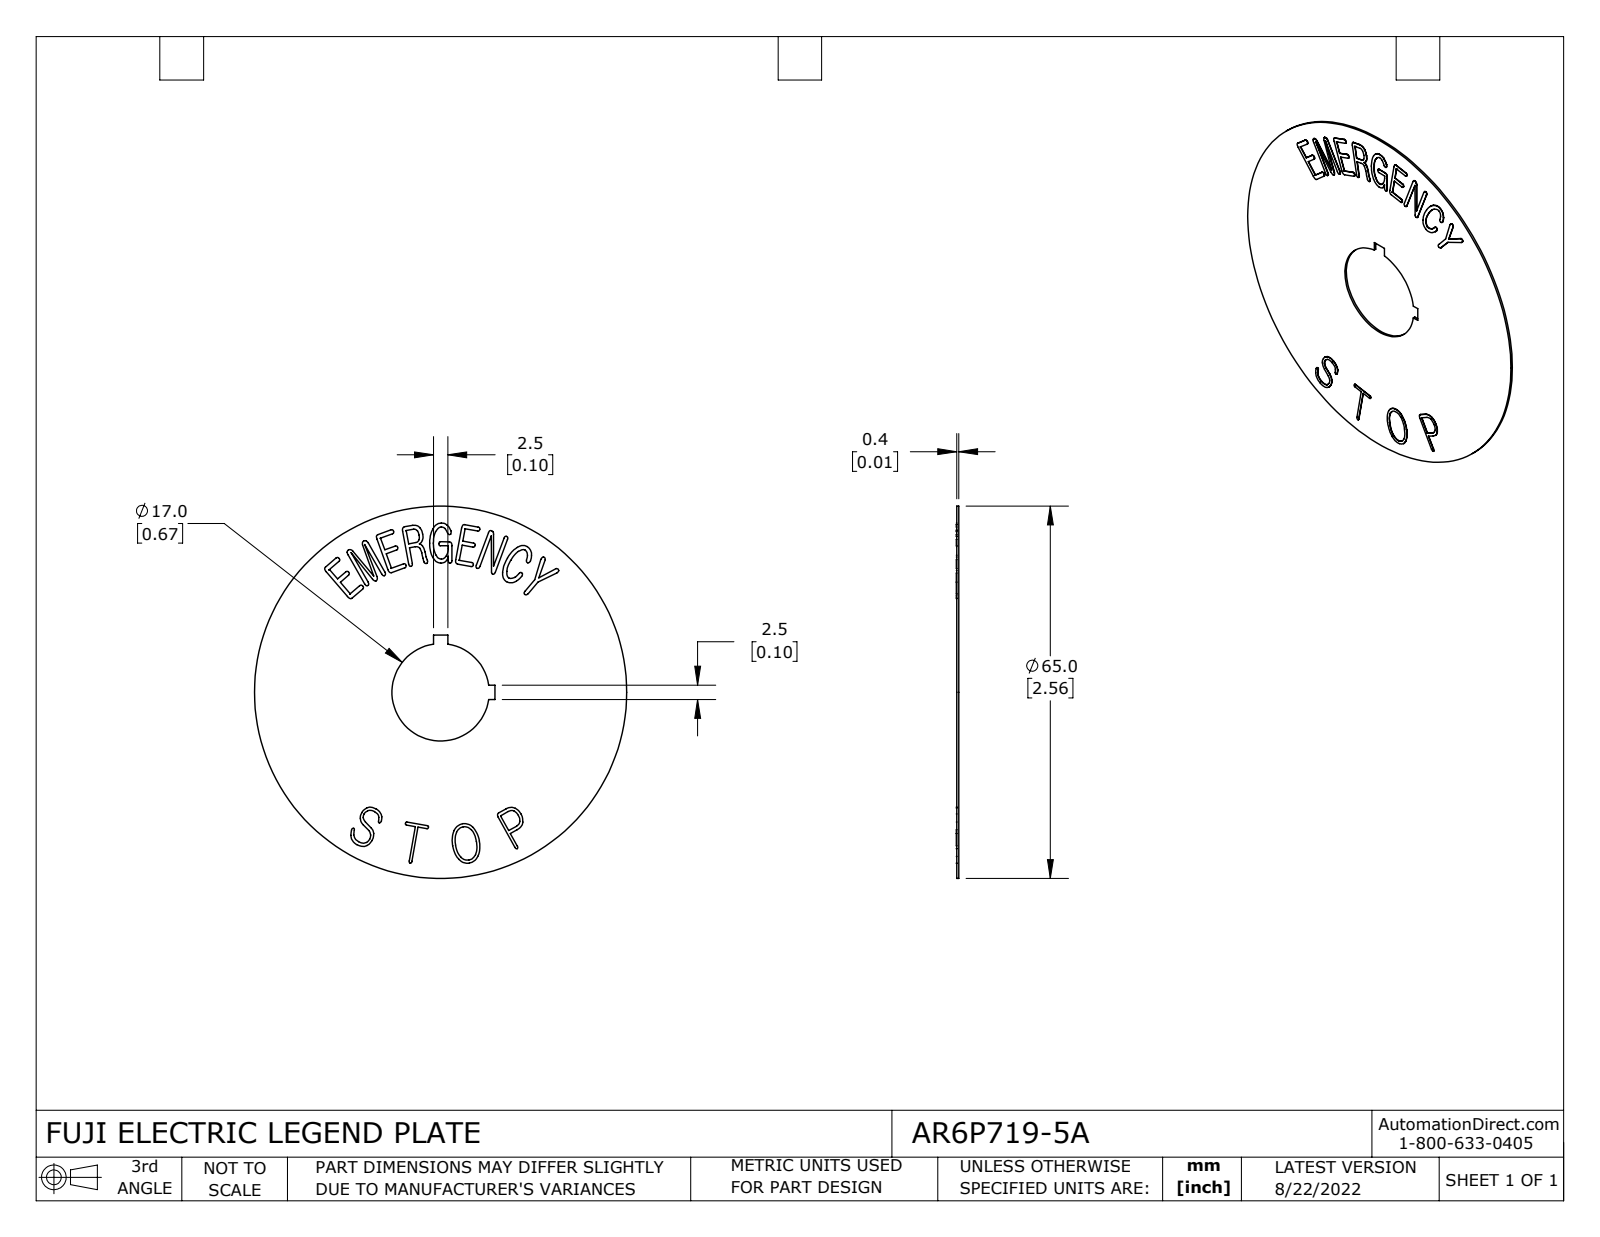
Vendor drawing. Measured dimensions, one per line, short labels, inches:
name: AR6P719-5A
written by: SolidWorks 2021 (CONFIG_CONTROL_DESIGN)
unit: in
bodies: 1 solid, 286 faces (97 planar, 5 cylindrical, 184 other)
size: 2.559 × 2.559 × 0.016
volume: 0.066 in³; area: 9.739 in²
holes: 1× ⌀0.669
bosses: 1× ⌀2.559
face distances: 0.014, 0.016, 0.098, 0.026, 0.135, 0.325, 0.423, 0.026, 0.443, 0.344
